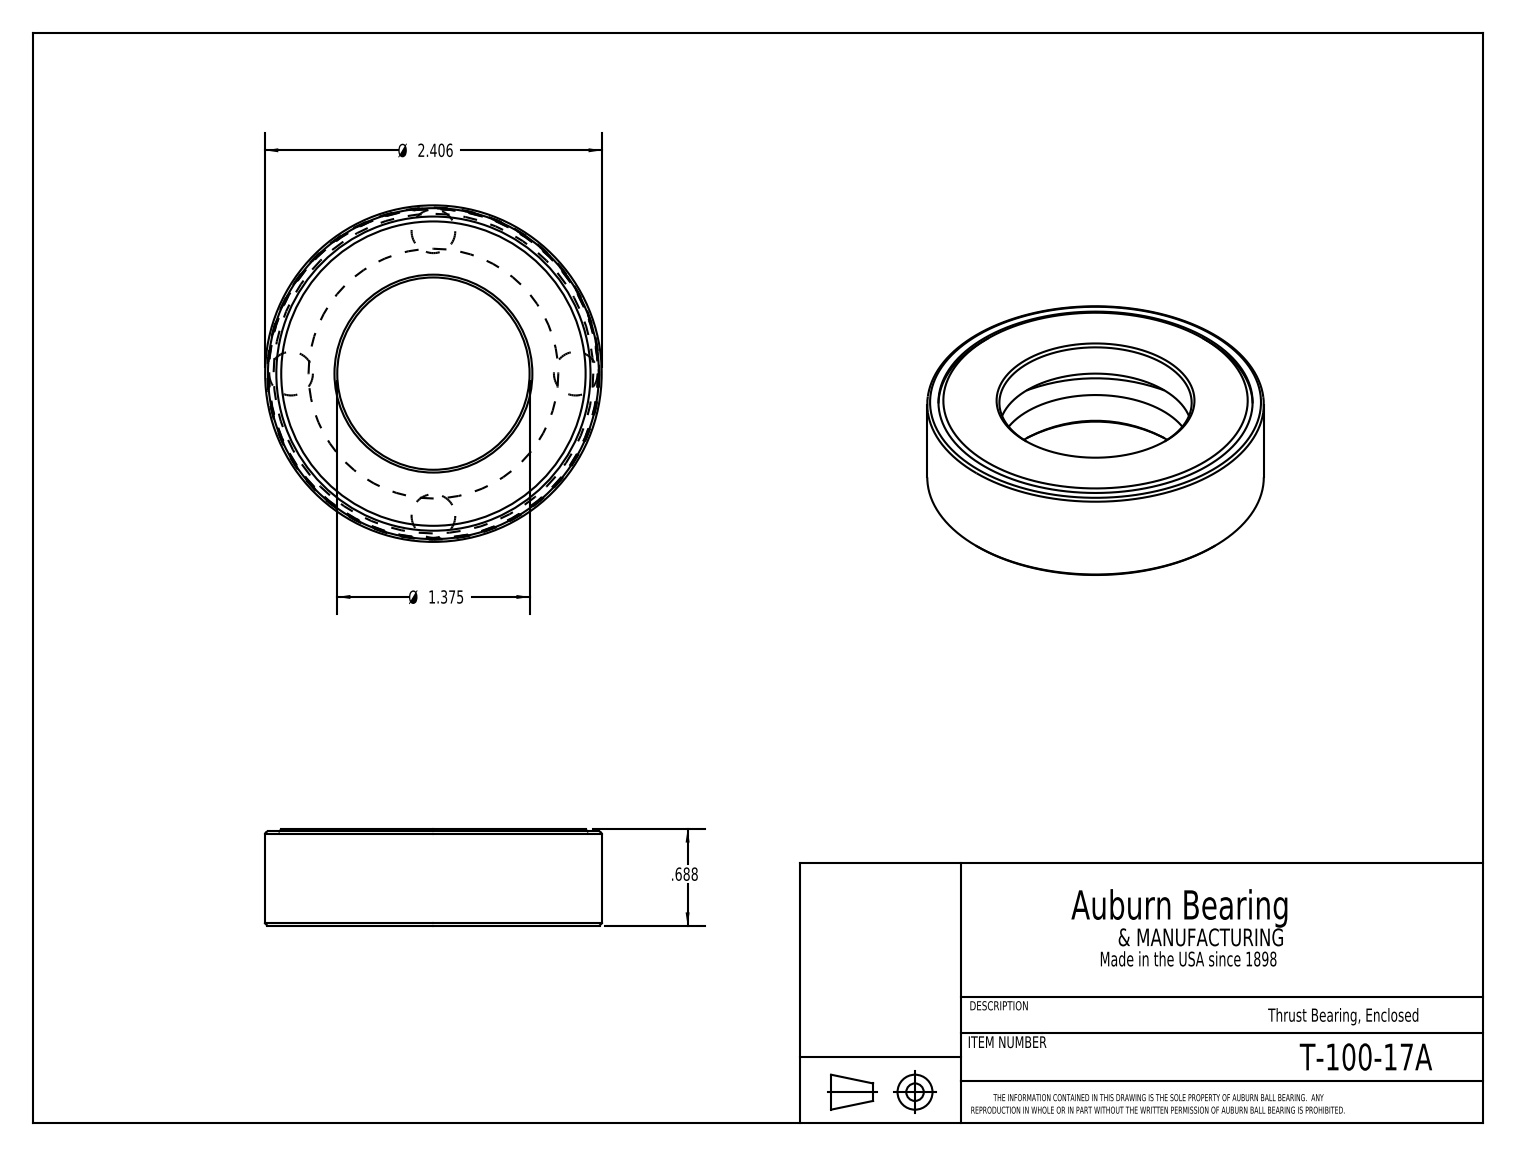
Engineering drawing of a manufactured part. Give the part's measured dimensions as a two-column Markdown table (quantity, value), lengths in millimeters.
| quantity | value |
| --- | --- |
| part name | T-100-17A |
| STEP written by | SolidWorks 2016 (CONFIG_CONTROL_DESIGN) |
| units | millimeters |
| bodies | 6 solids, 28 faces (9 planar, 7 cylindrical, 12 other) |
| overall size | 61.1 × 61.1 × 17.5 |
| volume | 23 700 mm³ |
| surface area | 16 850 mm² |
| round holes (diameter × count) | 34.9 × 1, 57 × 1, 60.1 × 1 |
| round bosses / shafts (diameter × count) | 61.1 × 1, 59.7 × 1 |
| main face-to-face distances | 6.4, 11.1, 17.4, 4.7, 16.6, 17.1, 10.2, 10.7, 5.5, 6 |
